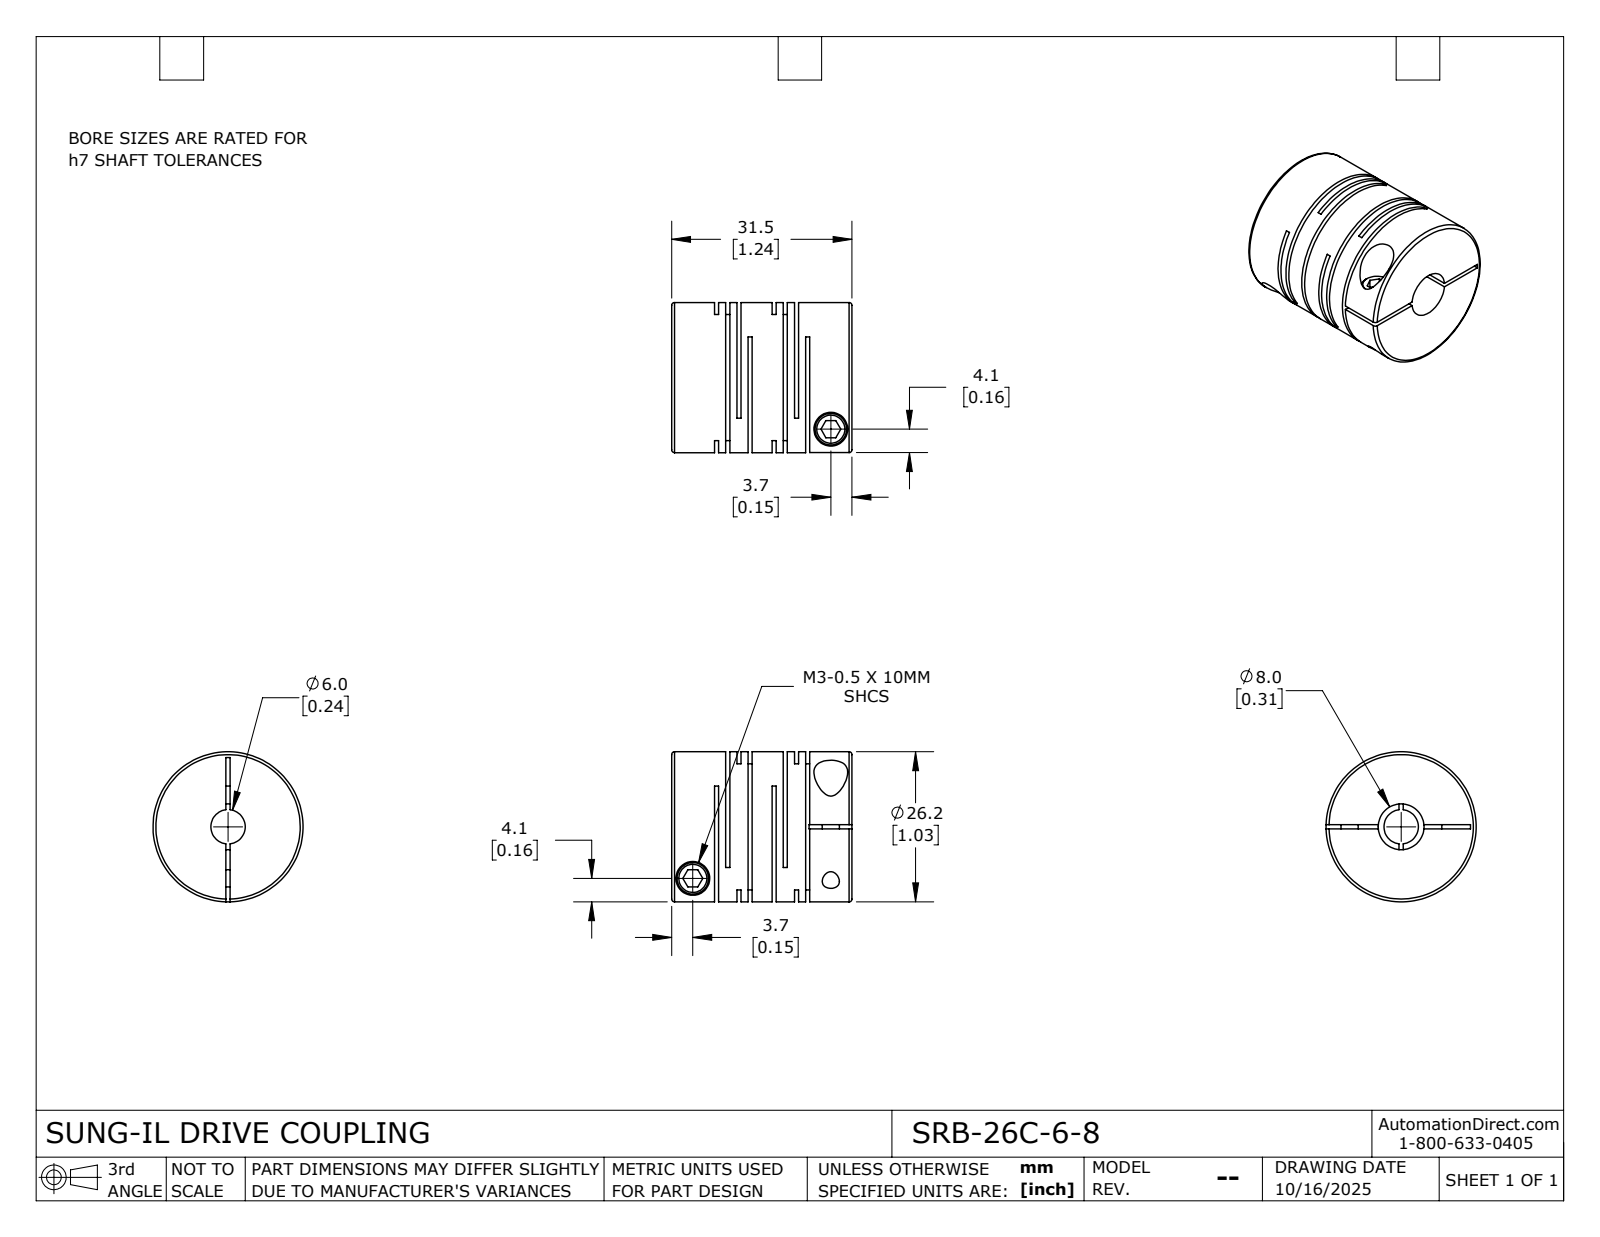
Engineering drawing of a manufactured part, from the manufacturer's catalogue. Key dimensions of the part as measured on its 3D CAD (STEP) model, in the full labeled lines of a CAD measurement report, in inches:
Part name (STEP PRODUCT): SRB-26C-6-8
STEP written by: SolidWorks 2024 (CONFIG_CONTROL_DESIGN)
Units: inches
Bodies: 1 solid, 115 faces (60 planar, 42 cylindrical, 13 other)
Overall size (bounding box): 1.24 × 1.031 × 1.031
Volume: 0.781 in³ · Surface area: 17.28 in²
Round holes (diameter × count): ⌀0.118 ×2, ⌀0.232 ×2, ⌀0.236 ×1, ⌀0.315 ×1
Round bosses / shafts (diameter × count): ⌀0.217 ×2, ⌀1.031 ×1
Main face-to-face distances: 0.077, 0.396, 0.028, 0.154, 0.319, 0.472, 0.049, 0.105, 0.368, 0.549
